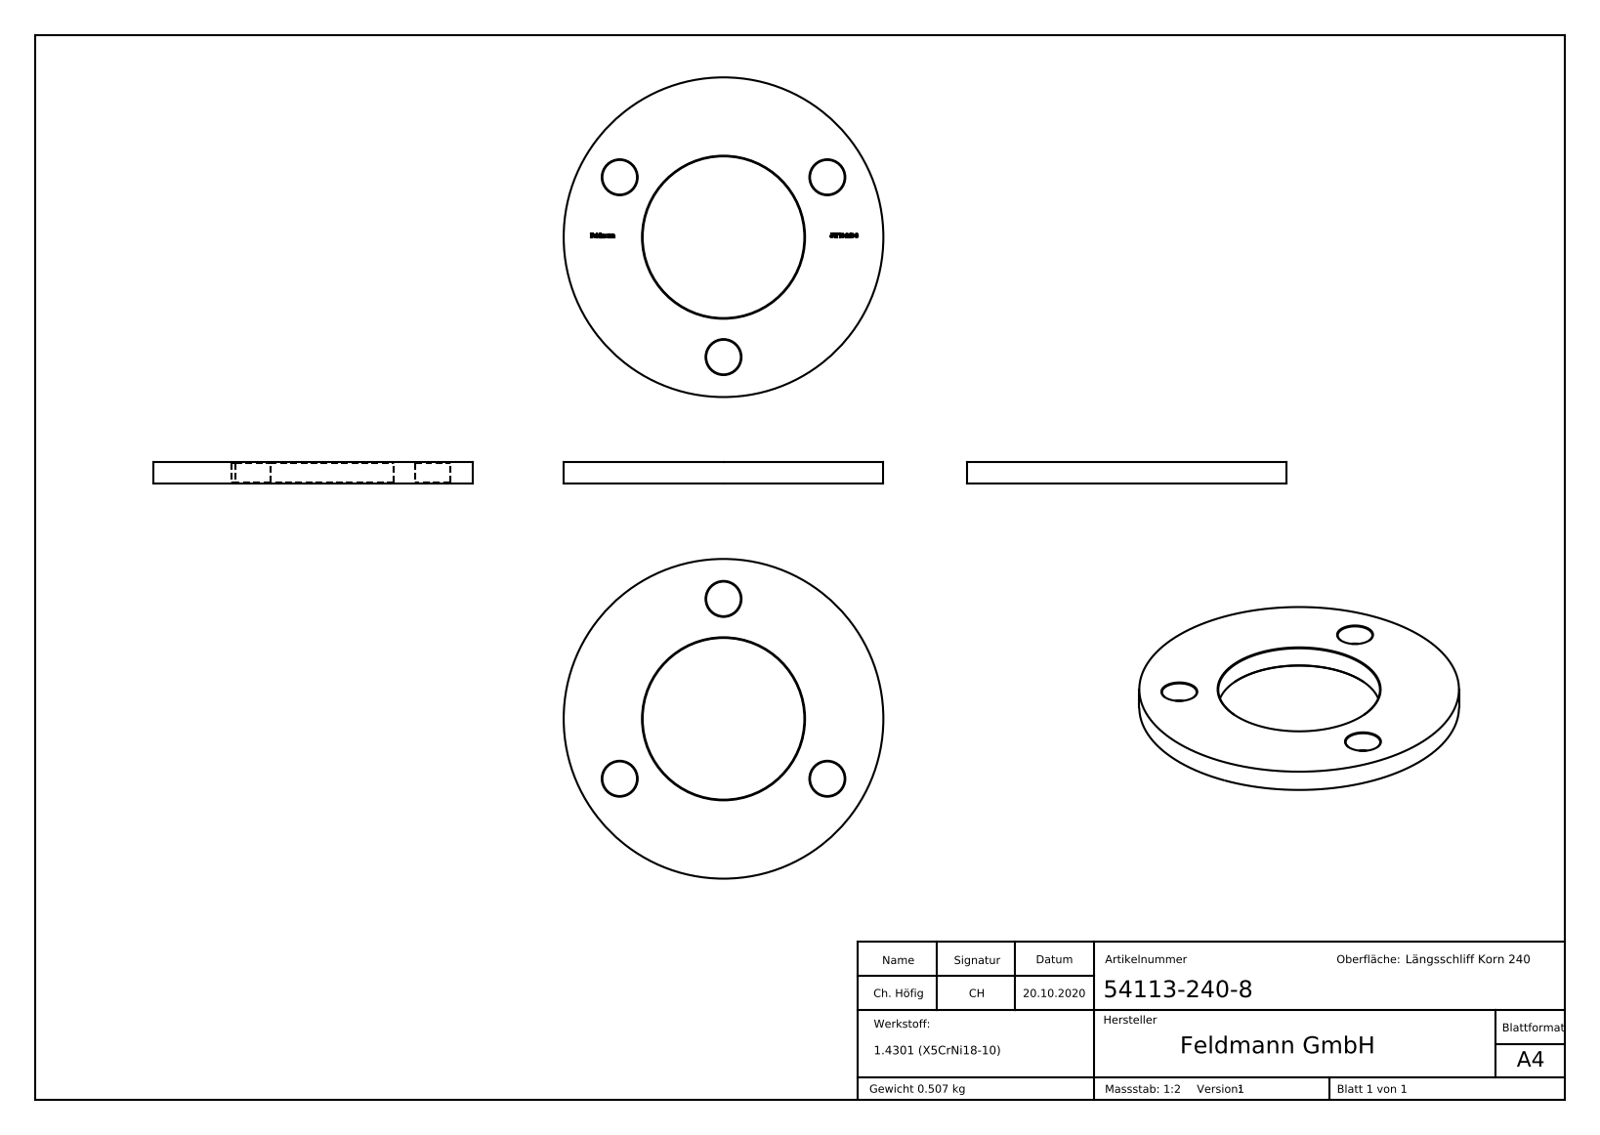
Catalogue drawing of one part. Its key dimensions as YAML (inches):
part_name: "54113-240-8"
step_written_by: "SolidWorks 2018 (CONFIG_CONTROL_DESIGN)"
units: inches
bodies: {solids: 1, faces: 272, planar: 144, cylindrical: 10, other: 118}
overall_size: [4.724, 4.724, 0.315]
volume: 3.913
surface_area: 33.29
round_holes:
  - {diameter: 0.512, count: 3}
  - {diameter: 2.39, count: 1}
round_bosses_or_shafts:
  - {diameter: 4.724, count: 1}
face_to_face_distances: [0.315, 0.311, 0.035, 0.017, 0.04, 0.023, 3.629, 3.669, 0.052, 3.519]
hole_center_spacings: [1.772, 3.069]
